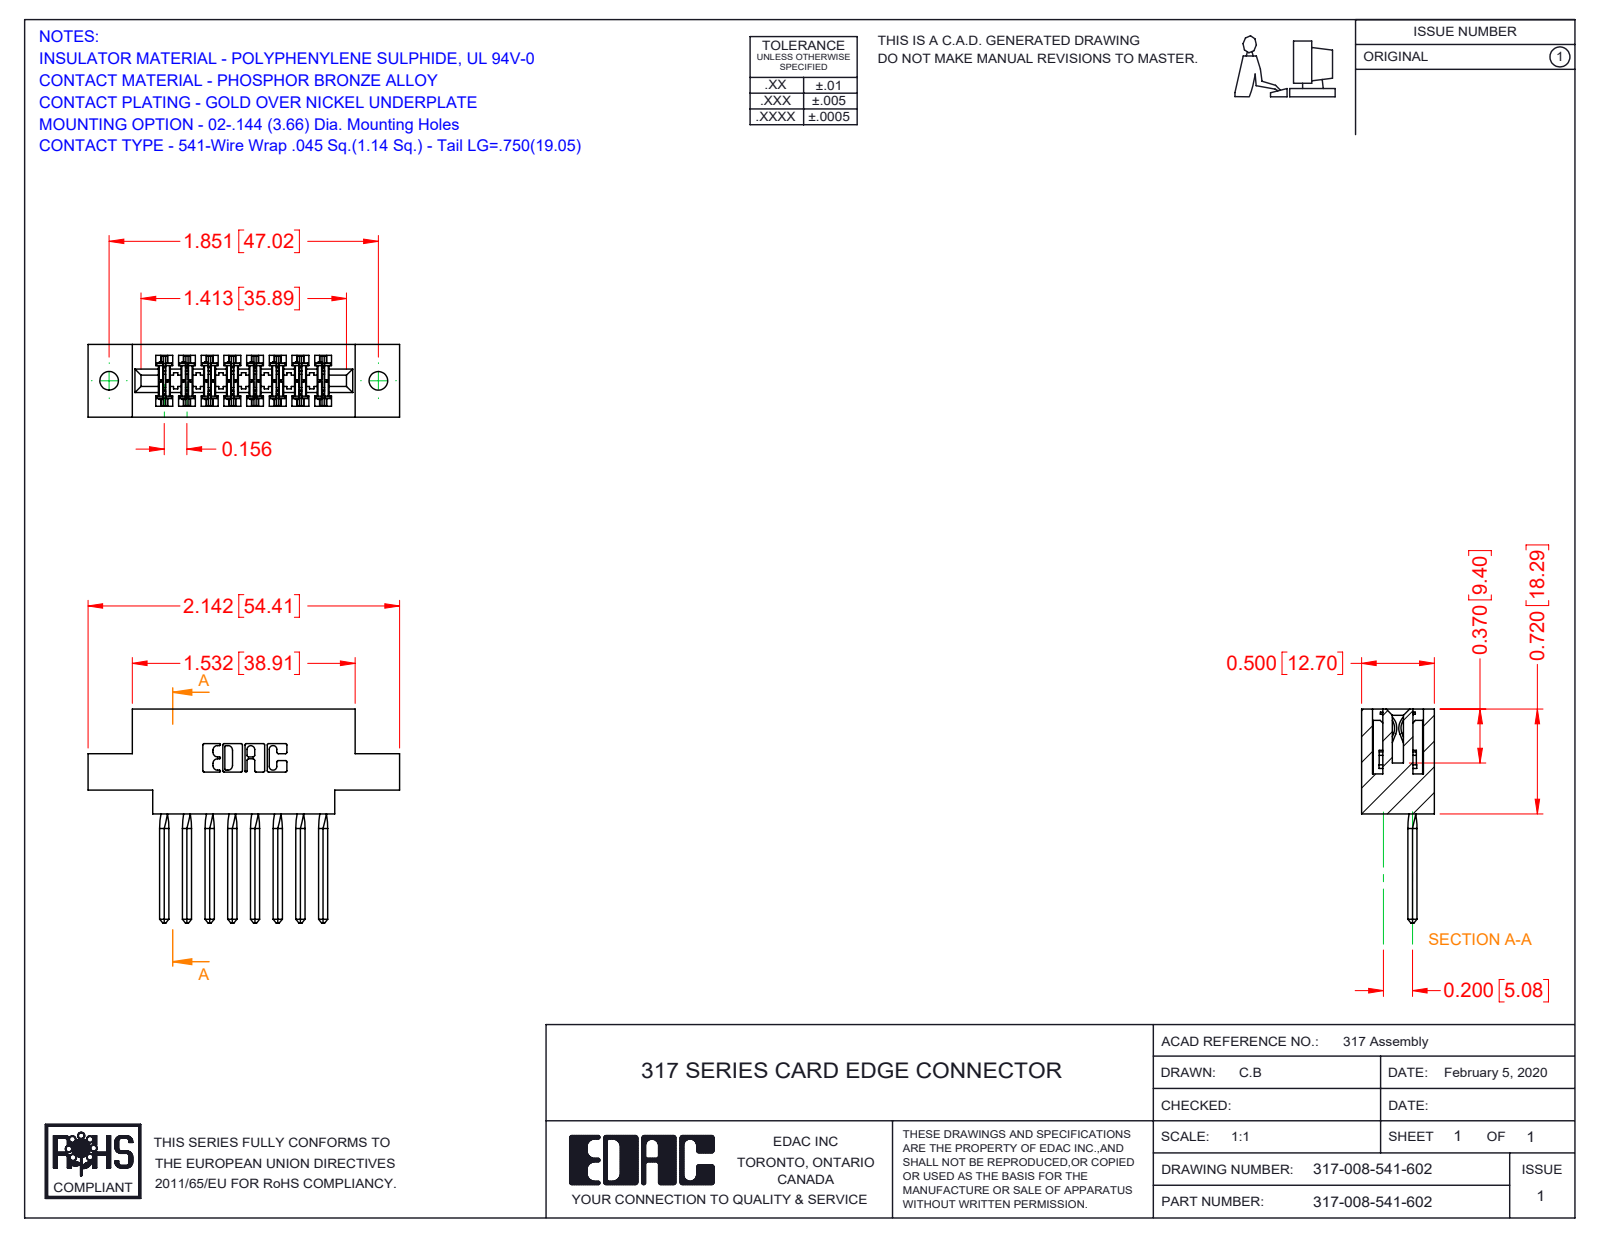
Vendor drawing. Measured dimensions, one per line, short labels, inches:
name: 317 Part_.144 Dia; 317-008-541-602; 317-290-002_541
written by: SolidWorks 2016 (CONFIG_CONTROL_DESIGN)
unit: in
bodies: 9 solids, 1318 faces (1050 planar, 236 cylindrical, 32 other)
size: 2.142 × 1.47 × 0.5
volume: 0.472 in³; area: 14.78 in²
holes: 2× ⌀0.128
rounds: 22× R0.01, 16× R0.015, 6× R0.007, 6× R0.031, 3× R0.026, 2× R0.095, 2× R0.1, 2× R0.11
face distances: 0.5, 0.075, 0.425, 0.11, 0.065, 0.22, 0.156, 0.331, 0.116, 0.35
hole spacings: 1.851
